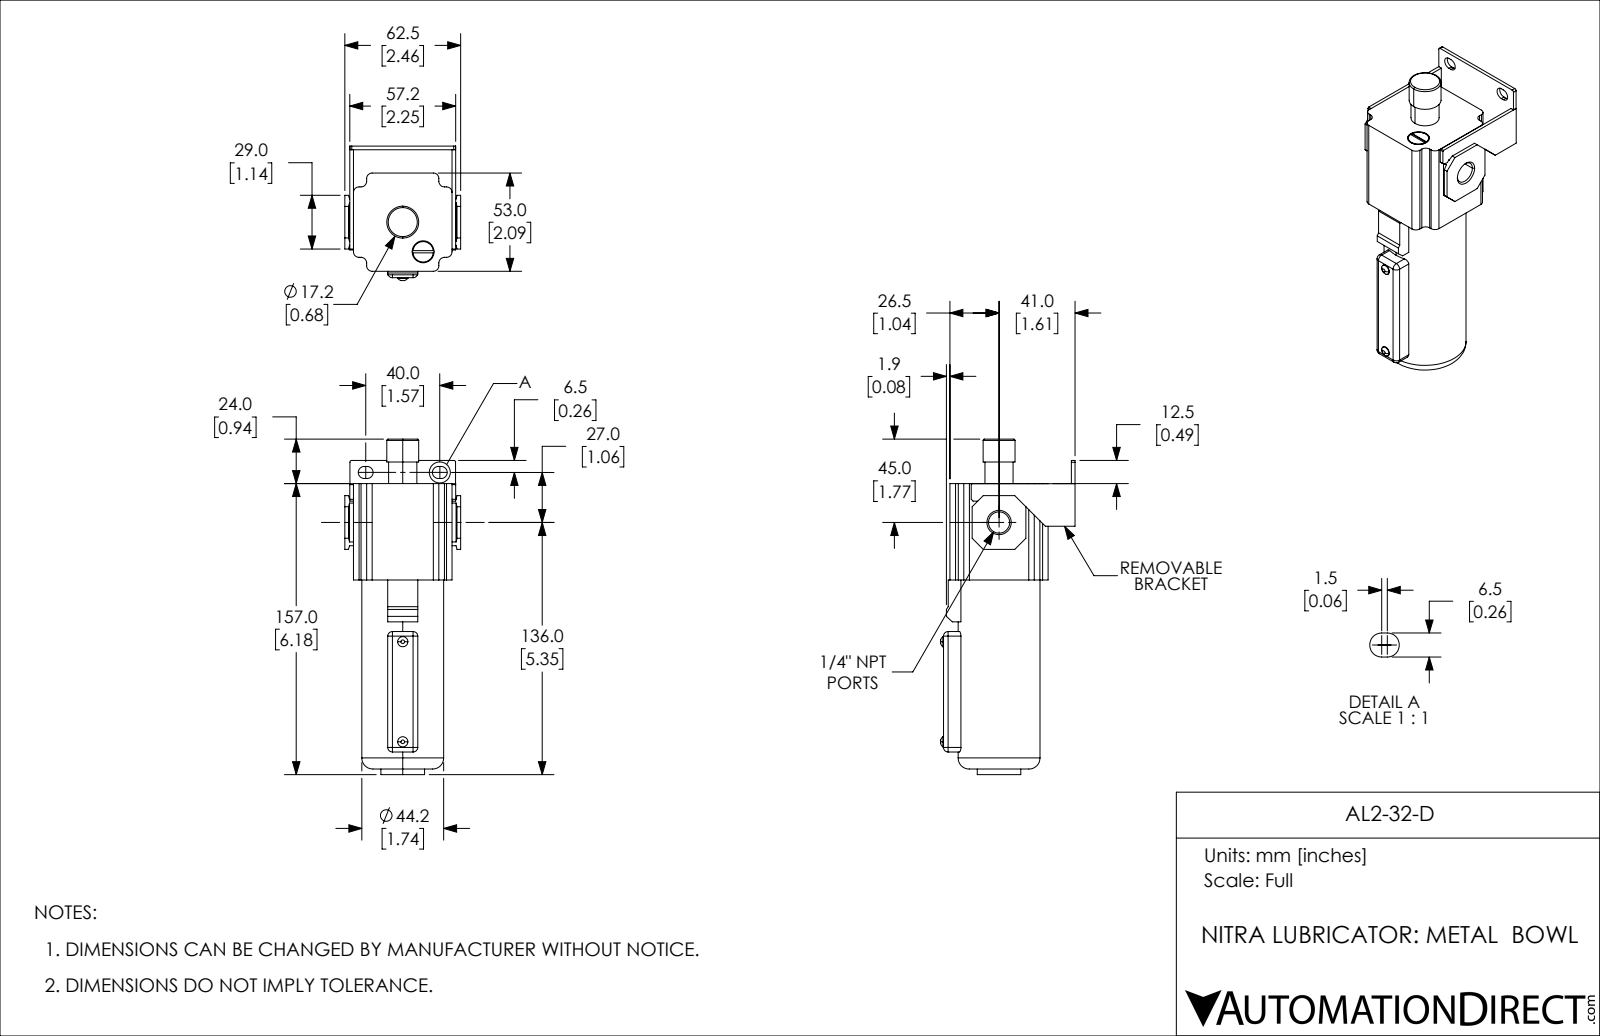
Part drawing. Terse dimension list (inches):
name: AL2-32-D
written by: SolidWorks 2019 (CONFIG_CONTROL_DESIGN)
unit: in
bodies: 1 solid, 162 faces (100 planar, 46 cylindrical, 16 other)
size: 7.126 × 2.854 × 2.461
volume: 19.43 in³; area: 63.95 in²
holes: 1× ⌀0.451, 1× ⌀0.465
bosses: 2× ⌀0.217, 1× ⌀1.74, 1× ⌀0.925, 1× ⌀0.677, 1× ⌀0.598, 1× ⌀0.433
rounds: 12× R0.118, 8× R0.098, 4× R0.128, 2× R0.039
face distances: 0.079, 0.492, 0.571, 2.657, 2.579, 2.087, 2.173, 0.104, 0.183, 2.278
